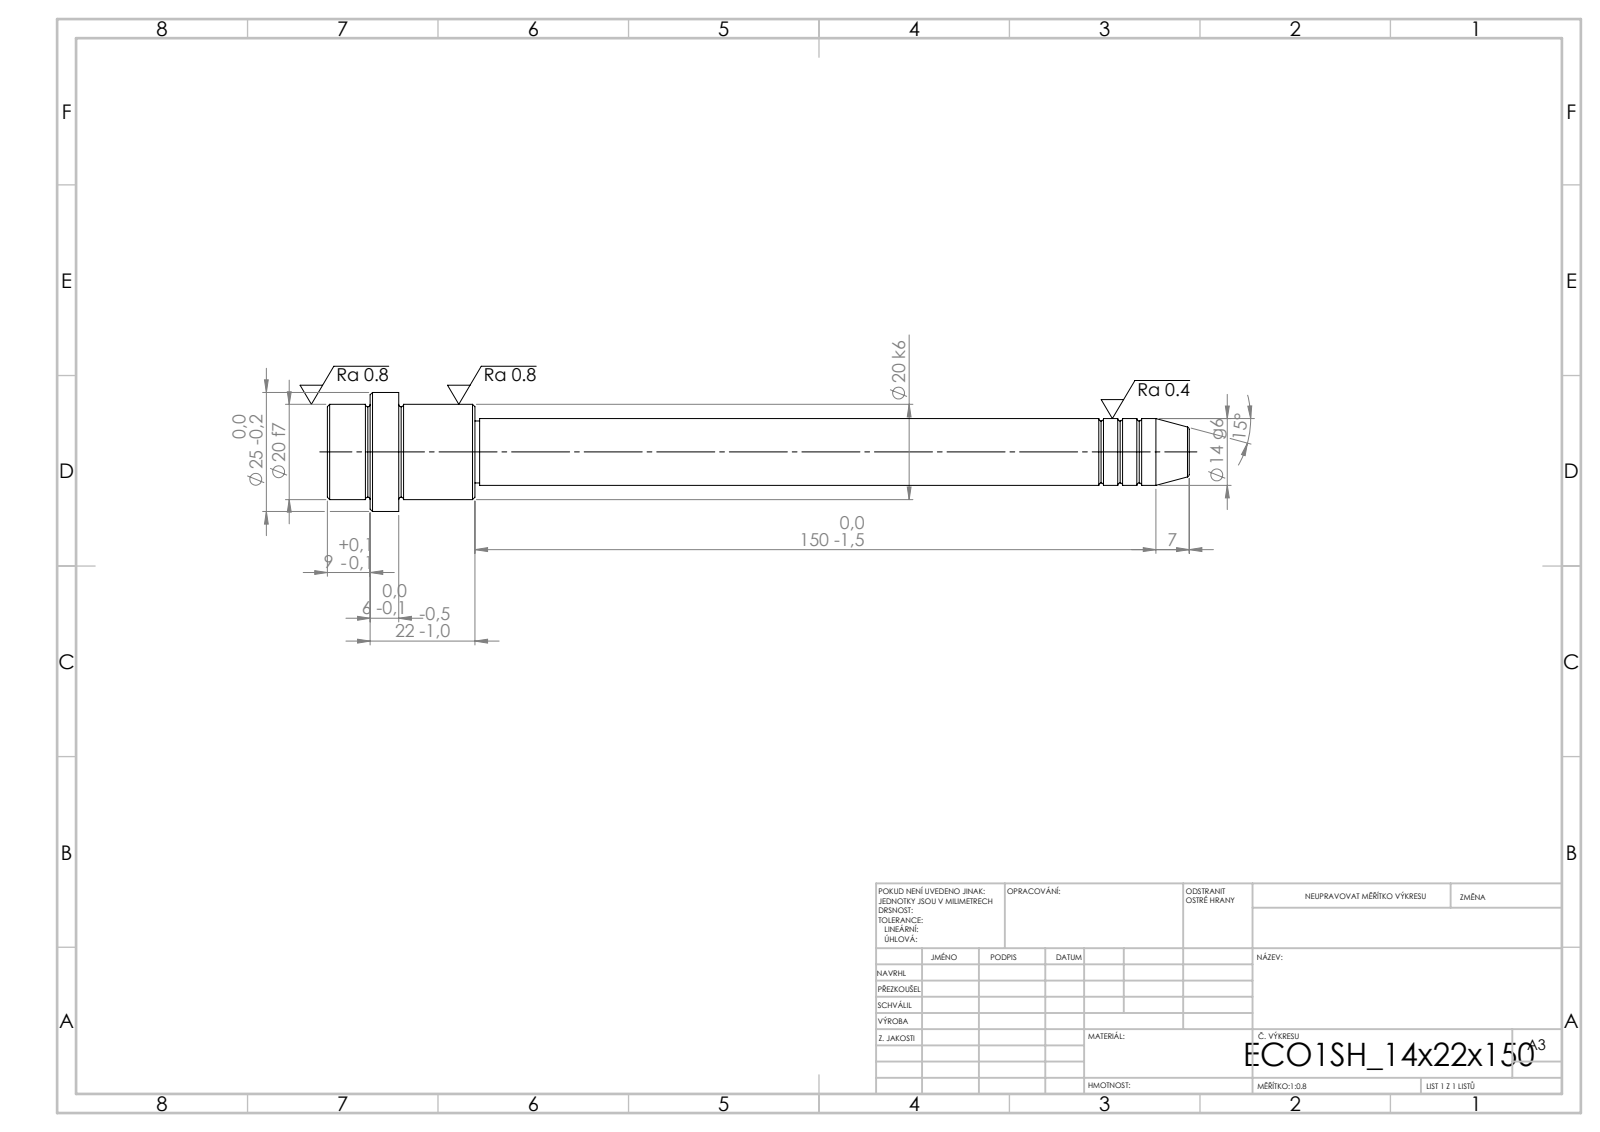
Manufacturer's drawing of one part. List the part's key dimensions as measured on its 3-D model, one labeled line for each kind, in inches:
STEP written by: SolidWorks 2019 (CONFIG_CONTROL_DESIGN)
Units: inches
Bodies: 1 solid, 52 faces (6 planar, 16 cylindrical, 30 other)
Overall size (bounding box): 7.126 × 0.984 × 0.984
Volume: 2.043 in³ · Surface area: 14.92 in²
Round bosses / shafts (diameter × count): ⌀0.984 ×1, ⌀0.787 ×1, ⌀0.551 ×1, ⌀0.512 ×1
Main face-to-face distances: 0.591, 0.63, 1.22, 0.866, 0.236, 0.354, 5.906, 6.535, 6.772, 7.126
